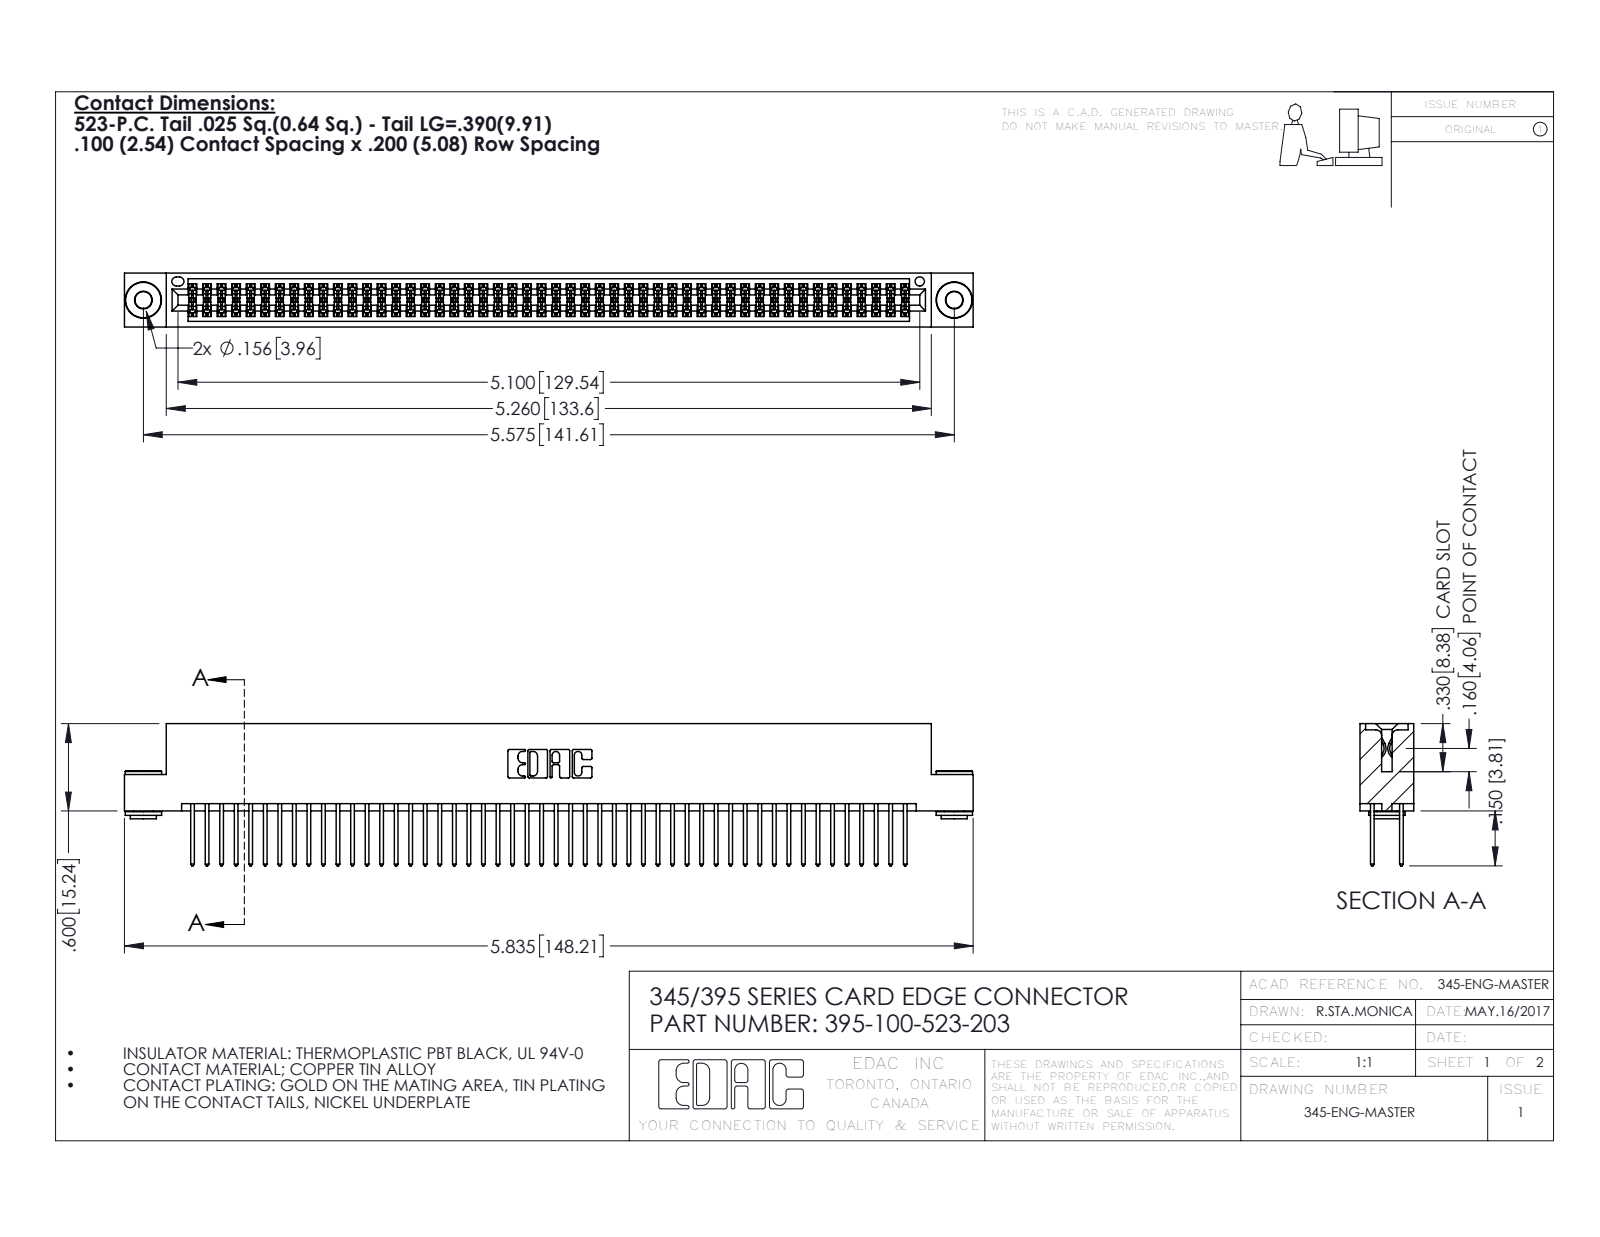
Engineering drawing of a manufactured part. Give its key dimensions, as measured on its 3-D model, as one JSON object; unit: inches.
{"part_name": "395-100-523-203; 345-250-002_345-250-002-102; 345-292-001_345-293-123; 345 Part_Flush Mounting Lugs - 0.156 Dia-TH", "step_written_by": "SolidWorks 2016 (CONFIG_CONTROL_DESIGN)", "units": "inches", "bodies": {"solids": 103, "faces": 5164, "planar": 3390, "cylindrical": 1766, "other": 8}, "overall_size": [5.835, 0.977, 0.37], "volume_in3": 0.897, "surface_area_in2": 35.65, "round_holes": [[0.116, 2], [0.156, 2], [0.064, 1]], "round_bosses_or_shafts": [[0.25, 2], [0.18, 2], [0.136, 2]], "partial_cylinders_radius": [[0.006, 150], [0.01, 100], [0.01, 22], [0.007, 6], [0.031, 6], [0.026, 3], [0.014, 2], [0.019, 2]], "face_to_face_distances": [0.072, 0.298, 0.2, 0.025, 0.098, 0.272, 0.37, 0.225, 0.175, 0.149], "hole_center_spacings": [0.27, 5.339, 5.575]}
